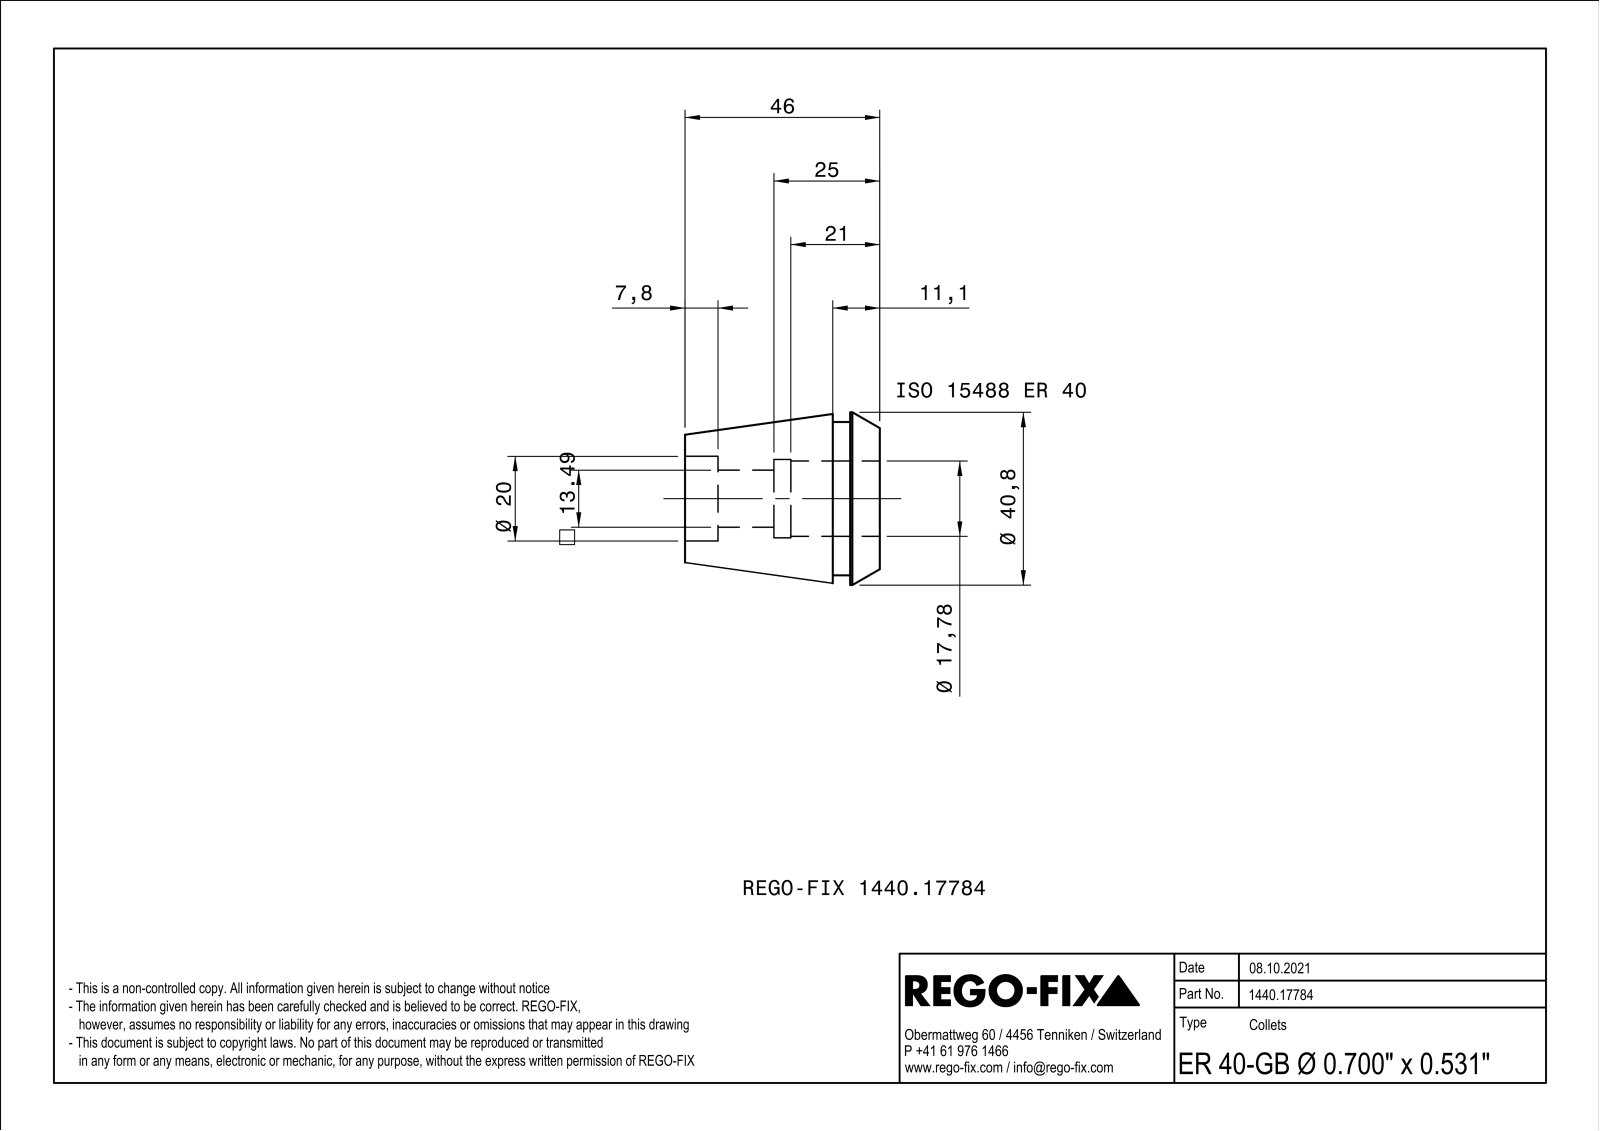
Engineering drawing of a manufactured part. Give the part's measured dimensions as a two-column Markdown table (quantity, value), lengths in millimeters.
| quantity | value |
| --- | --- |
| part name | NOCUT |
| STEP written by | SIEMENS PLM Software Solid Edge ST10 (AUTOMOTIVE_DESIGN) |
| units | millimeters |
| bodies | 1 solid, 152 faces (60 planar, 36 cylindrical, 56 other) |
| overall size | 46 × 40.79 × 40.79 |
| volume | 31 382 mm³ |
| surface area | 14 495 mm² |
| round holes (diameter × count) | 17.78 × 1, 18.5 × 1, 20 × 1 |
| round bosses / shafts (diameter × count) | 36.2 × 1 |
| partial cylindrical surfaces (radius × count) | 7.9 × 1, 9.15 × 1 |
| main face-to-face distances | 1, 46, 7.5, 7, 39, 6.5, 11.1, 4.1, 34.9, 14 |
